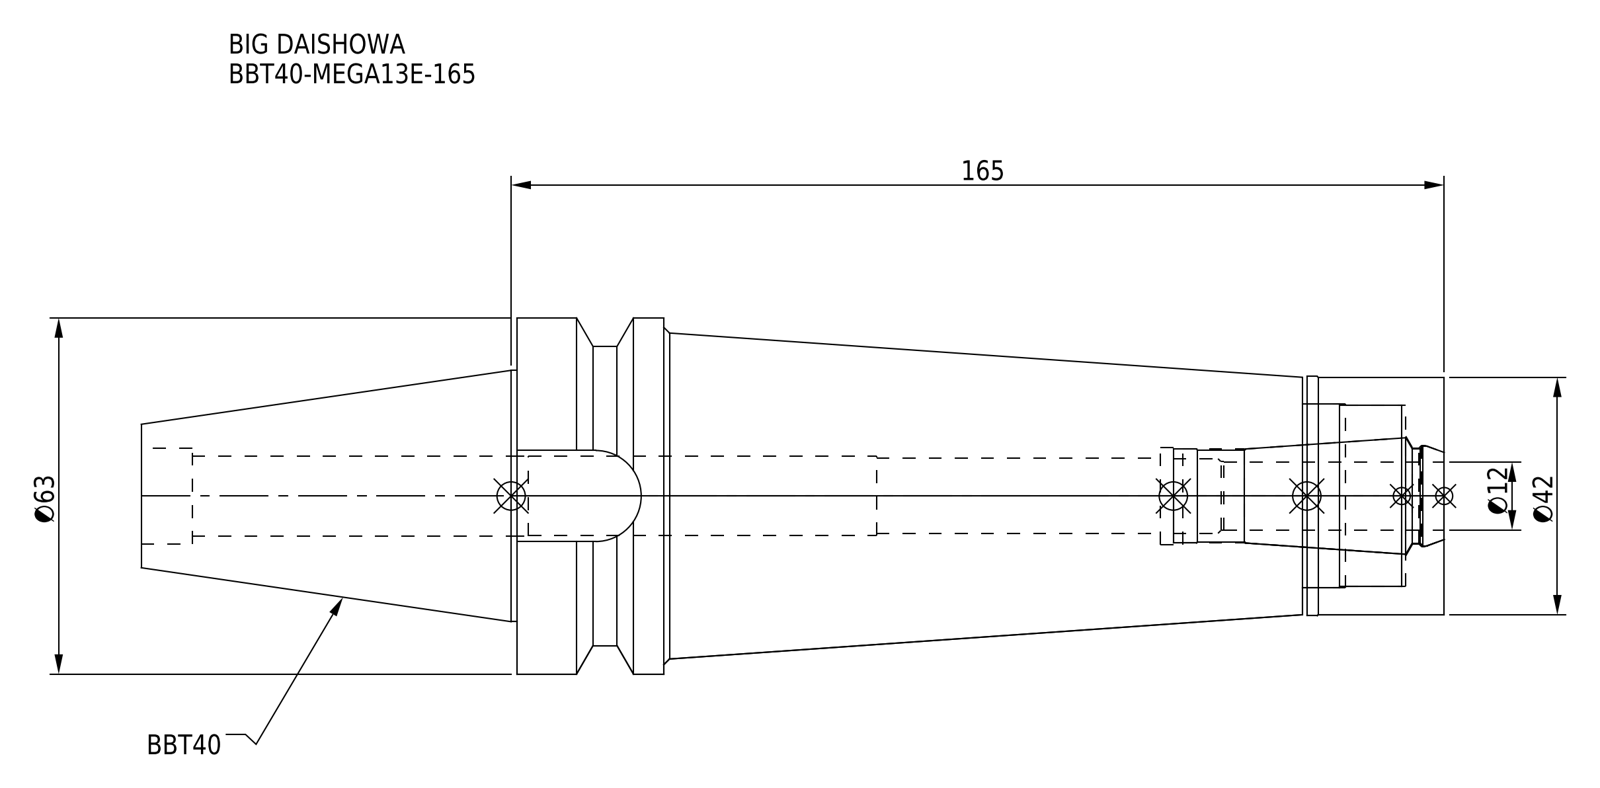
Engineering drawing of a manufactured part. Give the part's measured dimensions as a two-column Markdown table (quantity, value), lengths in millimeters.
| quantity | value |
| --- | --- |
| part name | BBT40-MEGA13E-165; DXF_TEMP_ASSY_ASM_4_ASM.stp; BBT40-MEGA13E-165_1.stp; BBT40ME13165-120_ASM.stp (+3 more) |
| STEP written by | SolidWorks 2019 (CONFIG_CONTROL_DESIGN) |
| units | millimeters |
| bodies | 2 solids, 81 faces (21 planar, 40 cylindrical, 20 other) |
| overall size | 230.4 × 63 × 63 |
| volume | 351 688 mm³ |
| surface area | 54 691 mm² |
| round holes (diameter × count) | 13.3 × 1, 14 × 1, 14.2 × 1, 16.6 × 1, 17 × 1, 17.2 × 1, 17.9 × 1, 32 × 1, 32.5 × 1 |
| round bosses / shafts (diameter × count) | 63 × 1, 53 × 1, 44.45 × 1, 42.3 × 1, 42 × 1 |
| partial cylindrical surfaces (radius × count) | 8.05 × 1 |
| main face-to-face distances | 164, 25.1, 24.3, 139.7, 0.8, 138.9, 6.8, 17.5, 7.5, 16.8 |
